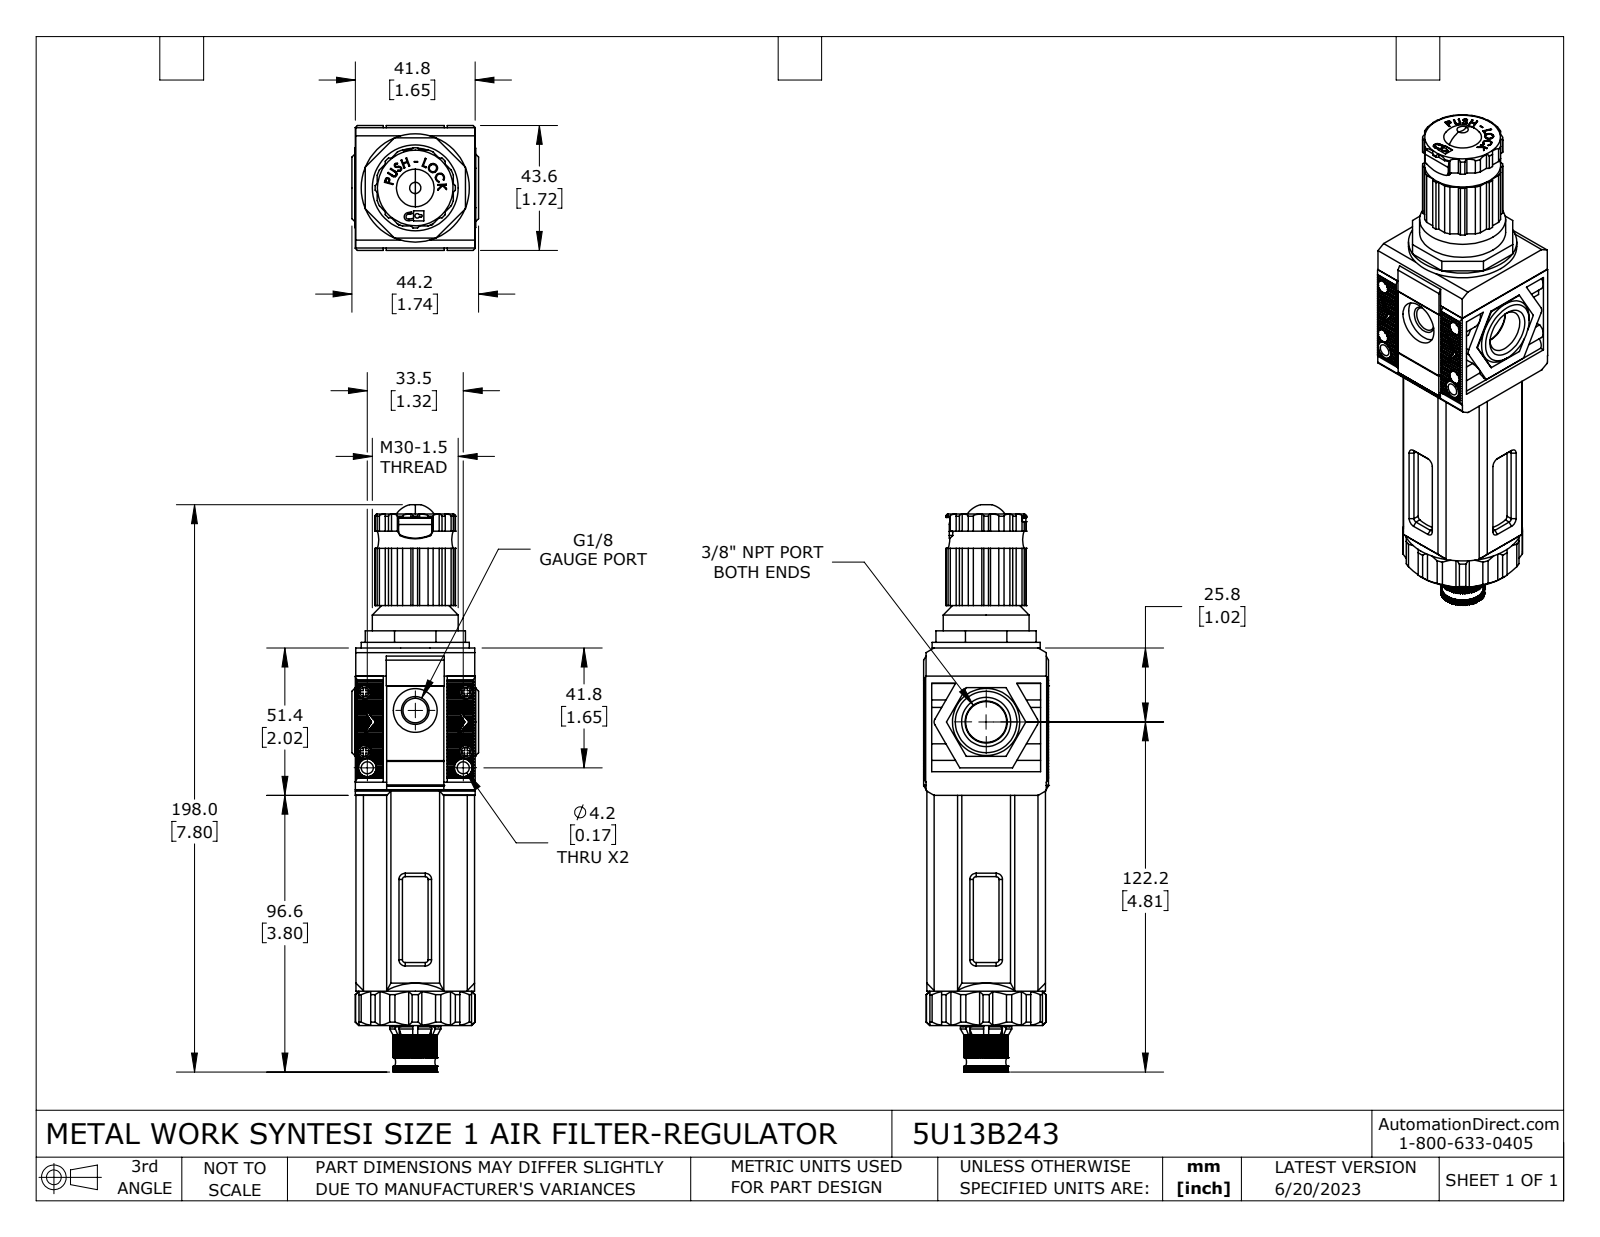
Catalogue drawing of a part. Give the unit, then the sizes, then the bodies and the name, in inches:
Units: inches
Overall size (bounding box): 7.795 × 1.74 × 1.717
Round holes (diameter × count): ⌀0.083 ×4, ⌀0.118 ×4, ⌀0.185 ×4, ⌀0.138 ×2, ⌀0.165 ×2, ⌀0.094 ×1, ⌀0.126 ×1, ⌀0.252 ×1, ⌀0.276 ×1, ⌀0.337 ×1, ⌀0.343 ×1, ⌀0.602 ×1
Round bosses / shafts (diameter × count): ⌀0.181 ×4, ⌀0.102 ×4, ⌀0.244 ×2, ⌀1.63 ×1, ⌀1.488 ×1, ⌀1.402 ×1, ⌀0.984 ×1, ⌀0.898 ×1
Partial cylindrical surfaces — rounded edges, fillets, slot ends (radius × count): R0.039 ×9, R0.024 ×4, R0.122 ×4, R0.059 ×3, R0.008 ×2, R0.051 ×2, R0.079 ×2, R0.016 ×1
Main face-to-face distances: 1.63, 1.638, 0.043, 1.673, 1.642, 0.307, 1.339, 1.575, 0.299, 1.331
Hole centre spacings: 0.222, 0.362, 0.742, 0.785, 0.823, 0.9, 1.027, 1.042
Volume: 9.809 in³ · Surface area: 115.1 in²
Bodies: 15 solids, 2177 faces (1612 planar, 418 cylindrical, 147 other)
Part name (STEP PRODUCT): 5U13B243
STEP written by: SolidWorks 2021 (CONFIG_CONTROL_DESIGN)
